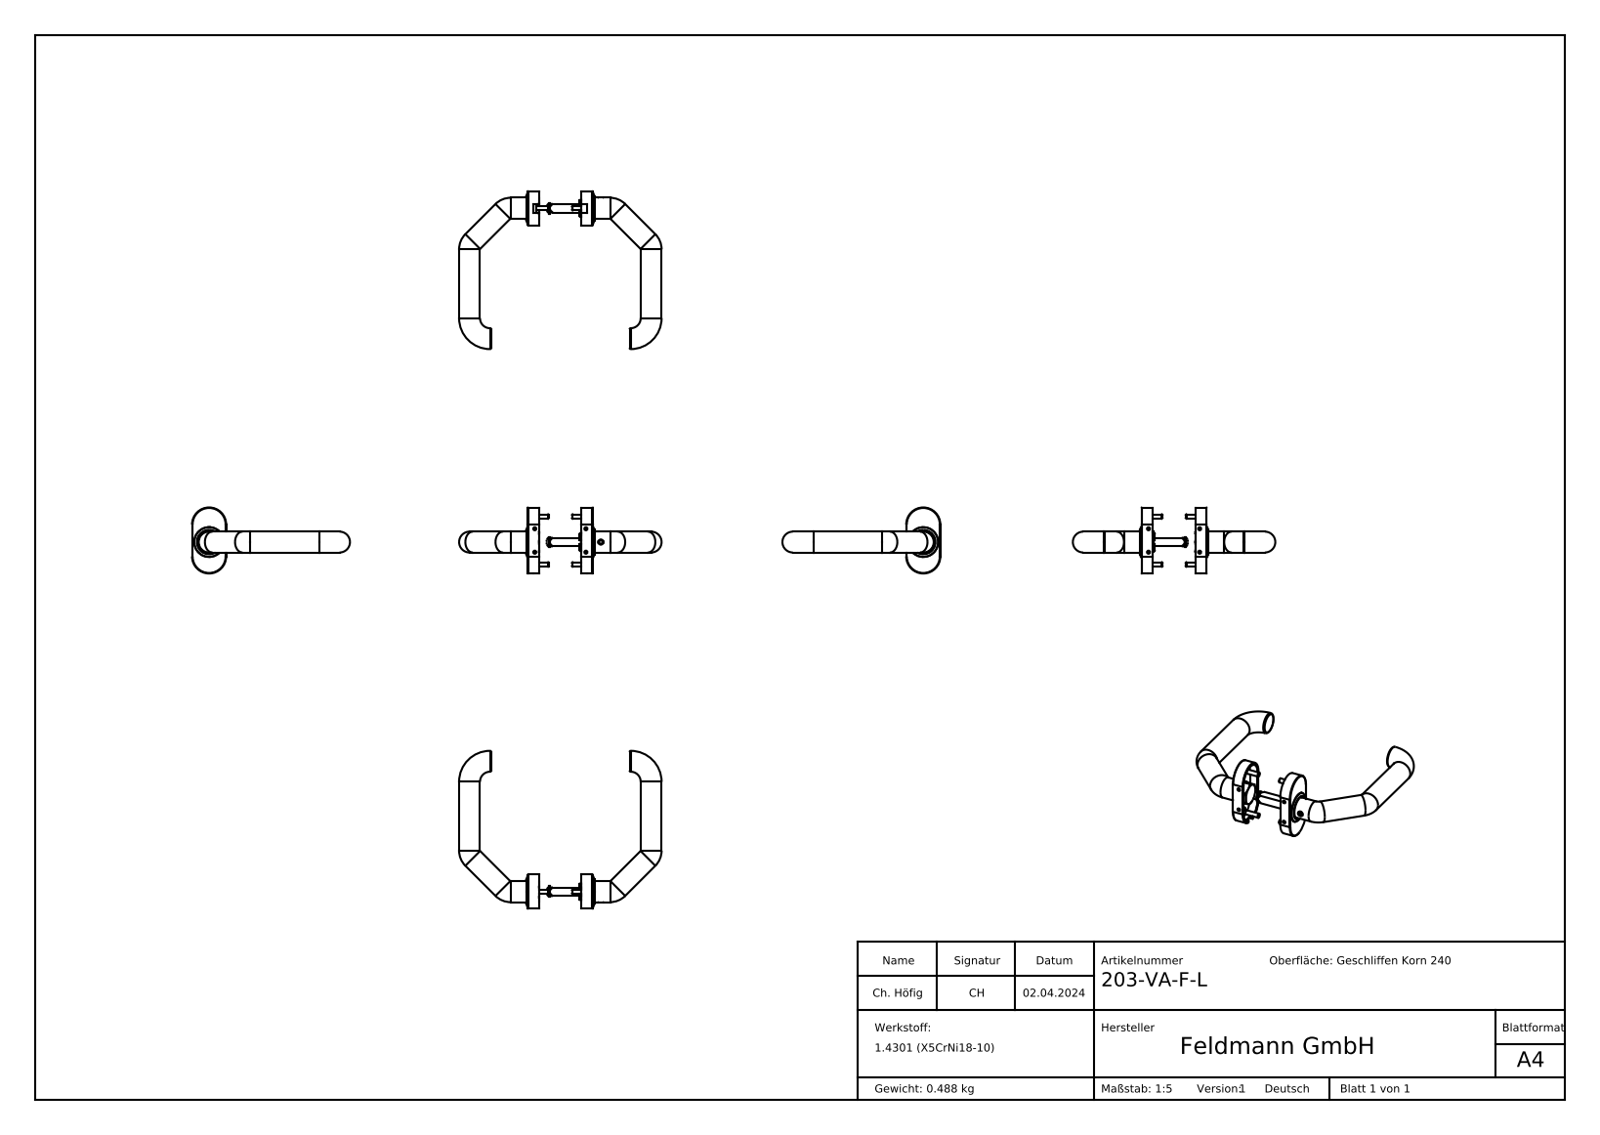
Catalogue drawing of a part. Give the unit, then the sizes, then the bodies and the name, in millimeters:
Units: millimetres
Overall size (bounding box): 190 × 148.2 × 62
Round holes (diameter × count): ⌀15.7 ×4, ⌀1.7 ×2, ⌀6.2 ×2, ⌀3.3 ×1, ⌀5 ×1, ⌀10 ×1, ⌀10.2 ×1, ⌀13.8 ×1, ⌀16 ×1, ⌀16.3 ×1, ⌀16.9 ×1, ⌀19.05 ×1
Round bosses / shafts (diameter × count): ⌀19.6 ×5, ⌀4 ×3, ⌀7.71 ×2, ⌀7.2 ×2, ⌀3.6 ×2, ⌀27.8 ×1, ⌀24 ×1, ⌀20.9 ×1
Partial cylindrical surfaces — rounded edges, fillets, slot ends (radius × count): R0.5 ×16, R0.78 ×4, R0.75 ×2, R2.5 ×2, R6.9 ×2, R8 ×2, R14 ×2, R15 ×2
Main face-to-face distances: 1, 0.9, 57, 2.5, 1.5, 58.5, 59.5, 58, 60.1, 0.6
Hole centre spacings: 8.88, 15.28, 29.81, 2.7, 21, 24, 45, 47.2
Volume: 66 255 mm³ · Surface area: 77 721 mm²
Bodies: 25 solids, 1118 faces (632 planar, 127 cylindrical, 359 other)
Part name (STEP PRODUCT): 603-VA-X-X Teil1 und 2_203-VA-F-L Teil1; DIN 967_M4x8; DIN 965_DIN 965 M4x18; 203-VA-F-L (+8 more)
STEP written by: SolidWorks 2018 (CONFIG_CONTROL_DESIGN)
